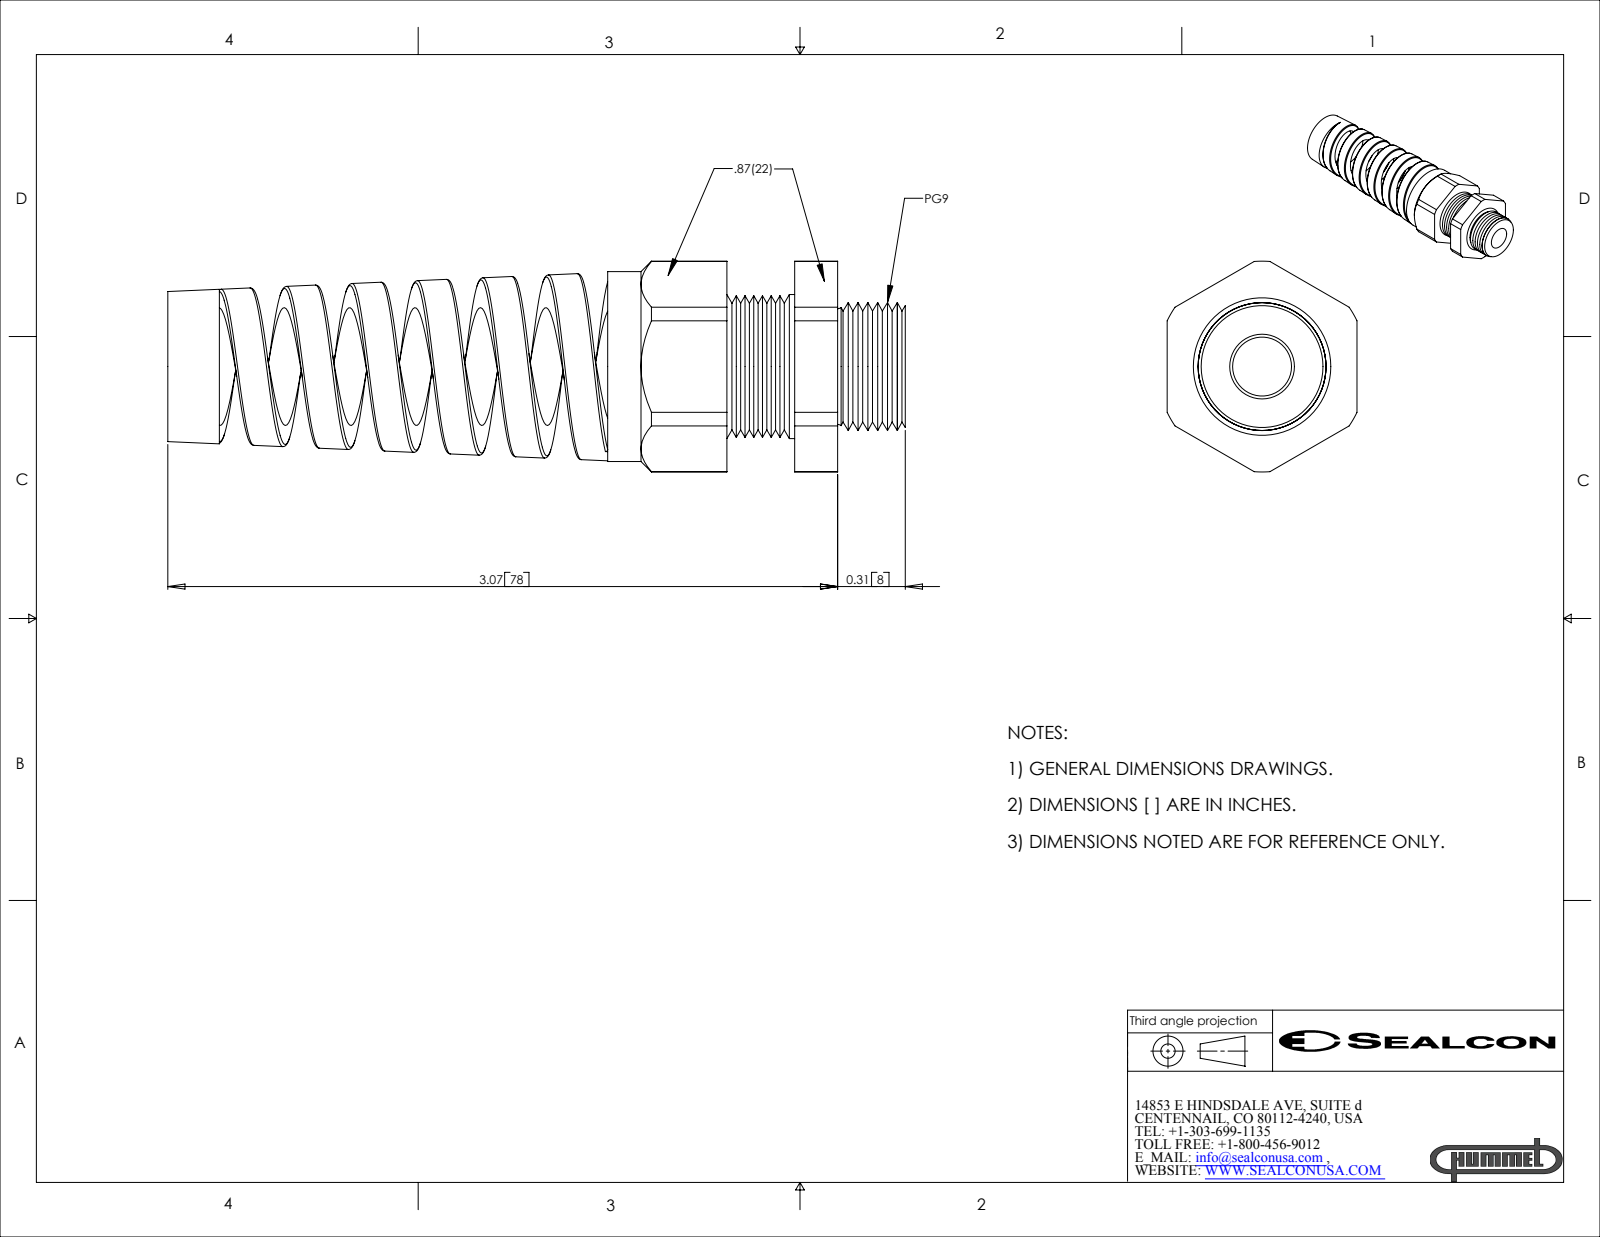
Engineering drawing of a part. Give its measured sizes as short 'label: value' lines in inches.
name: CF09GR-GY
written by: SolidWorks 2007 (CONFIG_CONTROL_DESIGN)
unit: in
bodies: 2 solids, 153 faces (24 planar, 37 cylindrical, 92 other)
size: 3.38 × 0.966 × 0.87
volume: 0.809 in³; area: 17.01 in²
holes: 1× ⌀0.27, 1× ⌀0.54
bosses: 1× ⌀0.87, 1× ⌀0.66
rounds: 1× R0.28, 1× R0.483
face distances: 0.87, 0.508, 0.311, 0.197, 0.818, 0.507, 0.31, 0.546, 0.857, 1.054
